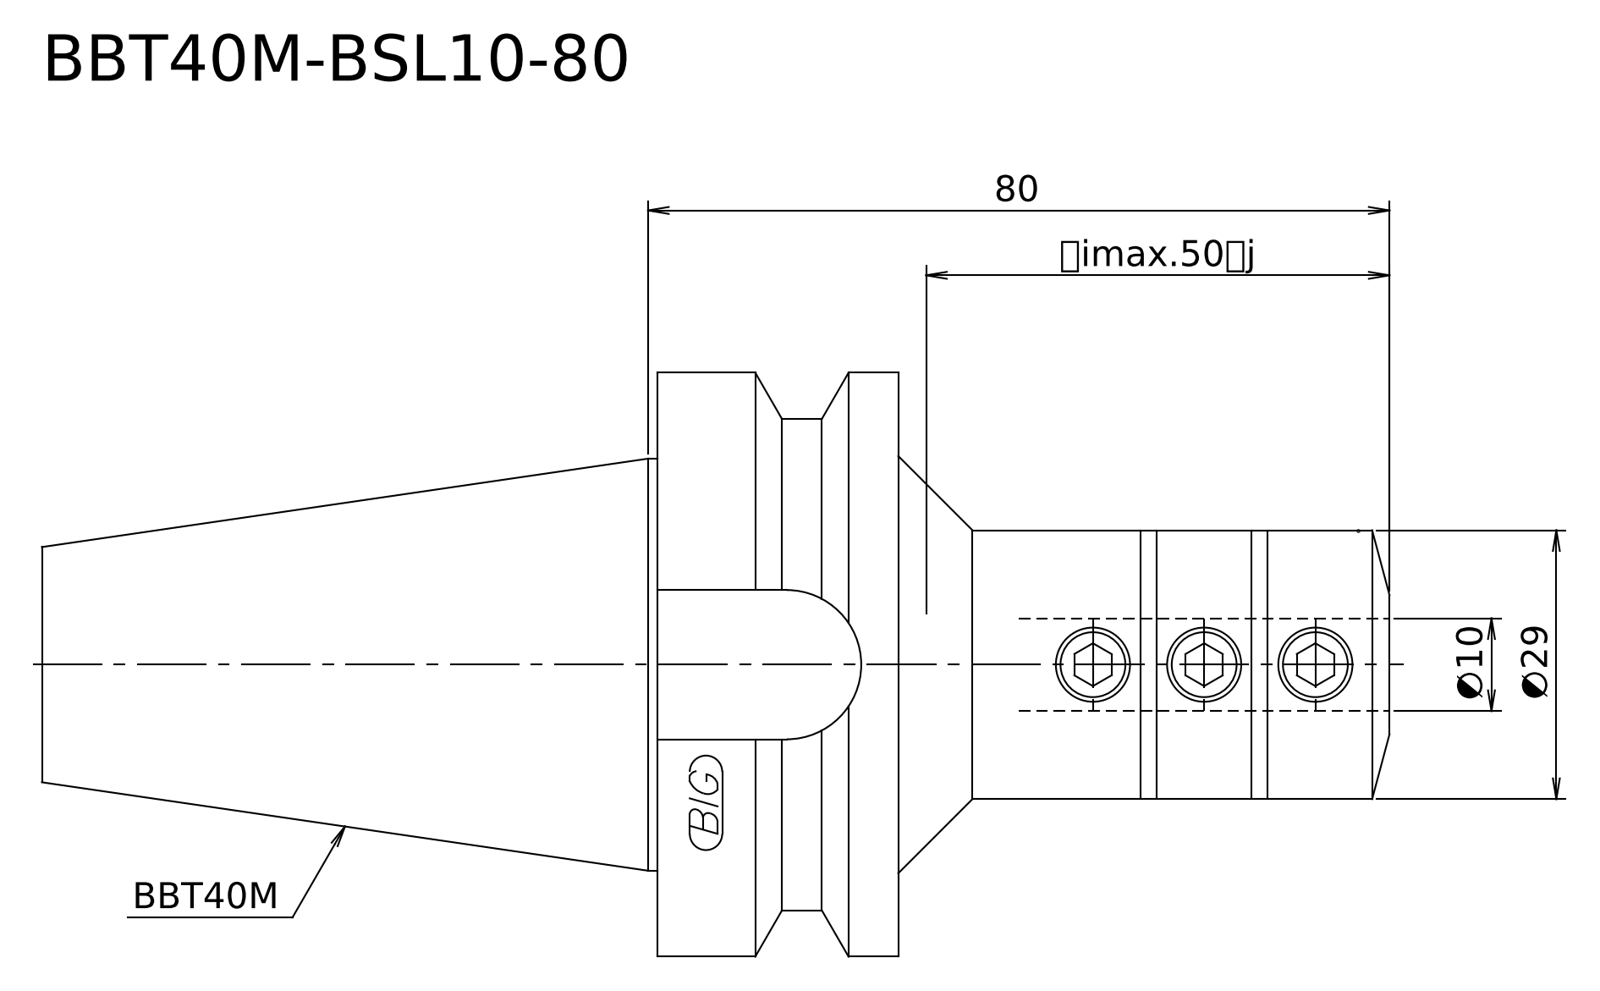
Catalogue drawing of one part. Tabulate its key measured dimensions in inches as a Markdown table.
| quantity | value |
| --- | --- |
| STEP written by | Kubotek KeyCreator 2011 V10.0.2 (22737) (automotive_design) |
| units | inches |
| bodies | 1 solid, 14 faces (4 planar, 5 cylindrical, 5 other) |
| overall size | 5.724 × 2.48 × 2.48 |
| volume | 10.87 in³ |
| surface area | 35.46 in² |
| round bosses / shafts (diameter × count) | 2.48 × 1, 2.087 × 1, 1.75 × 1, 1.142 × 1 |
| main face-to-face distances | 1.024, 3.638, 2.614, 2.087, 3.11, 5.724 |
